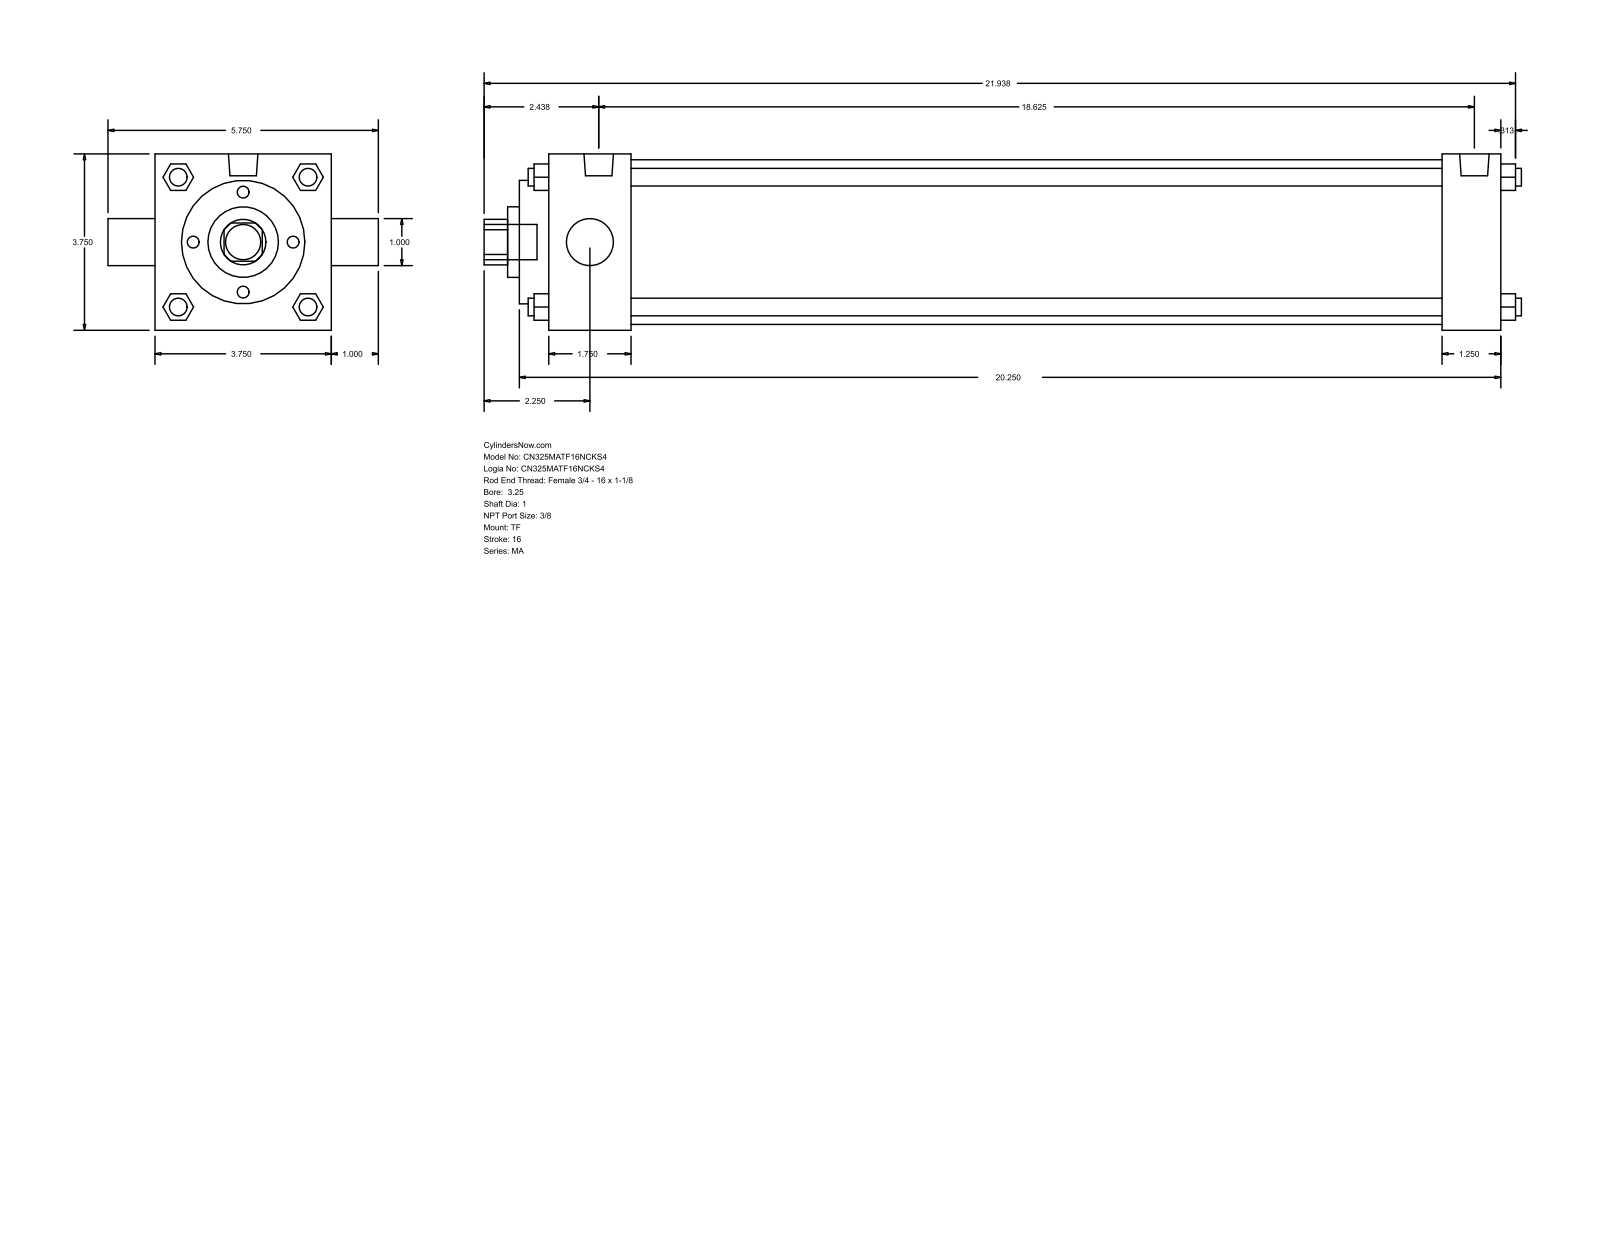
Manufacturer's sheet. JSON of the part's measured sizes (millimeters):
{"part_name": "MA_TF__0325_1", "step_written_by": "GSSL Pune (CONFIG_CONTROL_DESIGN)", "units": "millimeters", "bodies": {"solids": 0, "faces": 122, "planar": 93, "cylindrical": 29, "other": 0}, "overall_size": [560.39, 146.05, 95.25], "round_holes": [[25.4, 2], [38.1, 1], [66.67, 1], [88.9, 1]], "round_bosses_or_shafts": [[9.53, 4], [11.11, 3], [15.93, 2], [19.05, 1]], "partial_cylinders_radius": [[12.29, 1]], "face_to_face_distances": [95.24, 514.35, 530.22, 15.87, 44.46, 482.6, 438.14, 469.89, 31.75, 60.33]}
